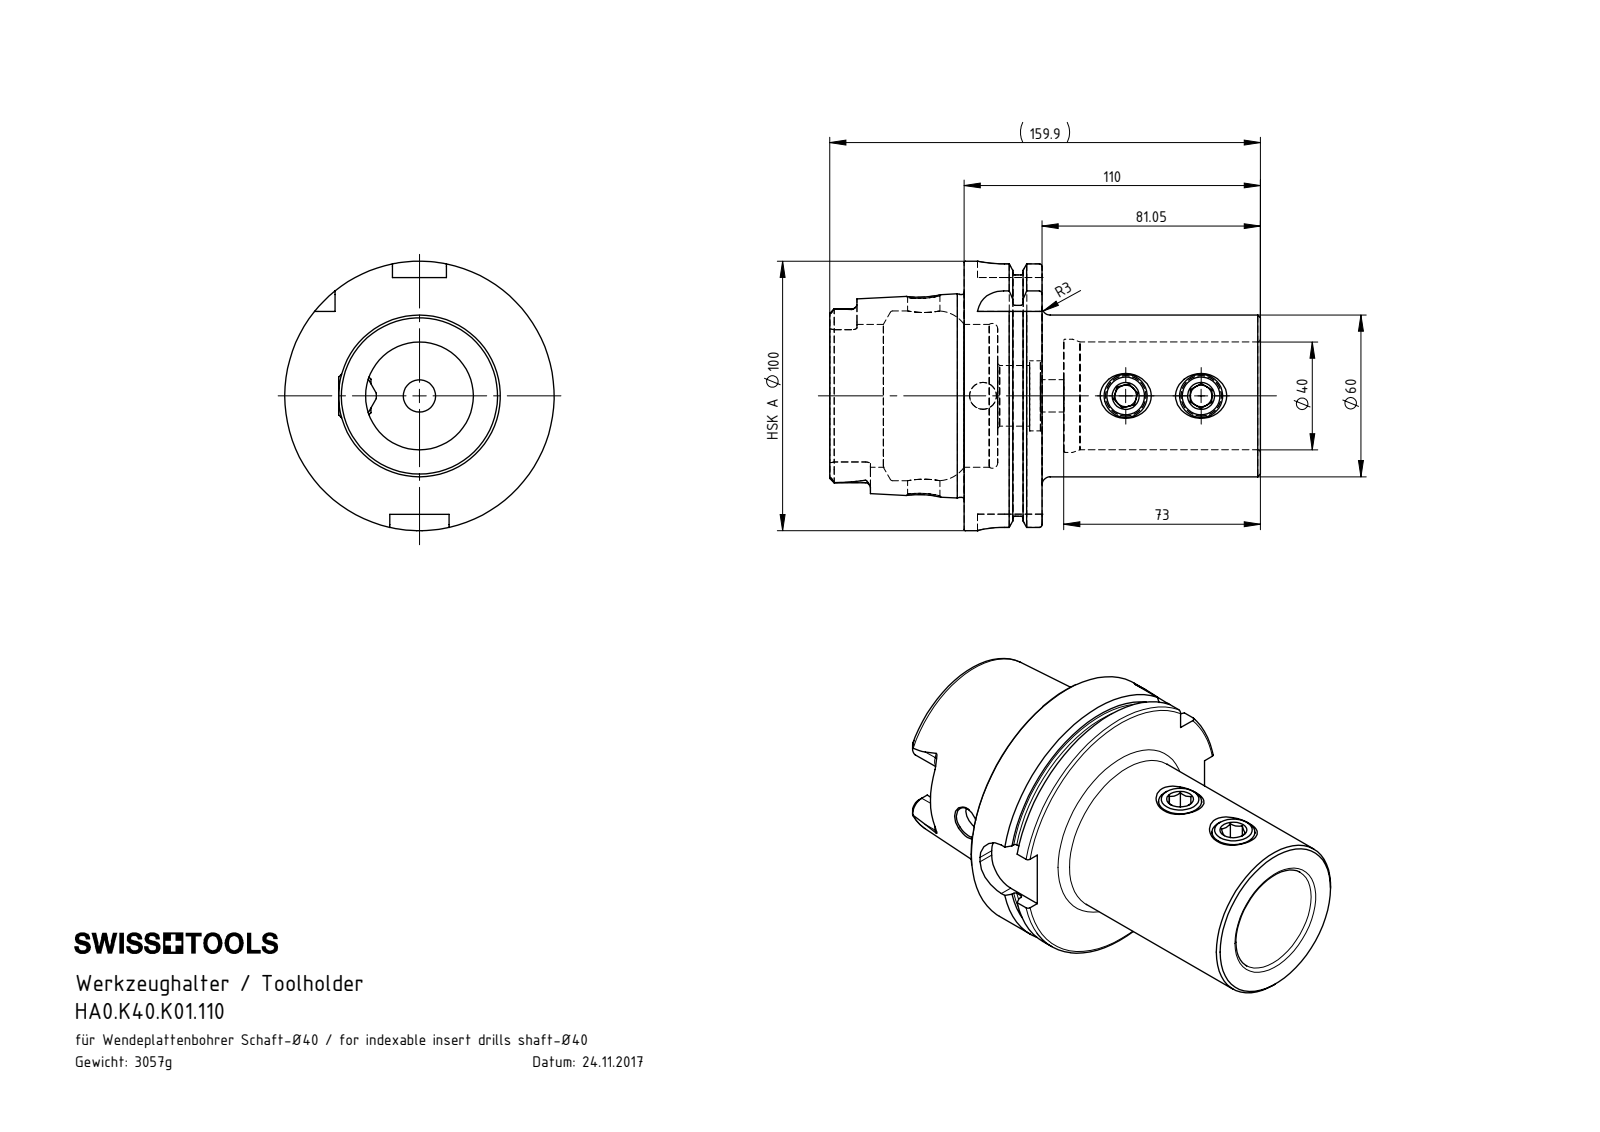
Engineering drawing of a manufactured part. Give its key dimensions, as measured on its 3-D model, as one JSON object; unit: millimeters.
{"part_name": "K40-ER1.016.012; HA0-K40.K01.110_A_Fertigbearbeitung; K40-ER2.016.014_PreviewCfg; HA0-K40.K01.110", "step_written_by": "SolidWorks 2017 (CONFIG_CONTROL_DESIGN)", "units": "millimeters", "bodies": {"solids": 3, "faces": 224, "planar": 69, "cylindrical": 62, "other": 93}, "overall_size": [159.9, 100, 100], "volume_mm3": 389368, "surface_area_mm2": 76421, "round_holes": [[8, 2], [12, 2], [15, 2], [10, 1], [22.5, 1], [26, 1], [40, 1], [42, 1], [53, 1], [63, 1]], "round_bosses_or_shafts": [[16, 2], [100, 1], [91.95, 1], [75.26, 1], [60, 1]], "partial_cylinders_radius": [[1.9, 6], [10, 4], [4.83, 2], [4.88, 2]], "face_to_face_distances": [28.95, 12.45, 16.5, 110, 97.55, 81.05, 37, 24.55, 8.05, 73], "hole_center_spacings": [28, 53, 81]}
